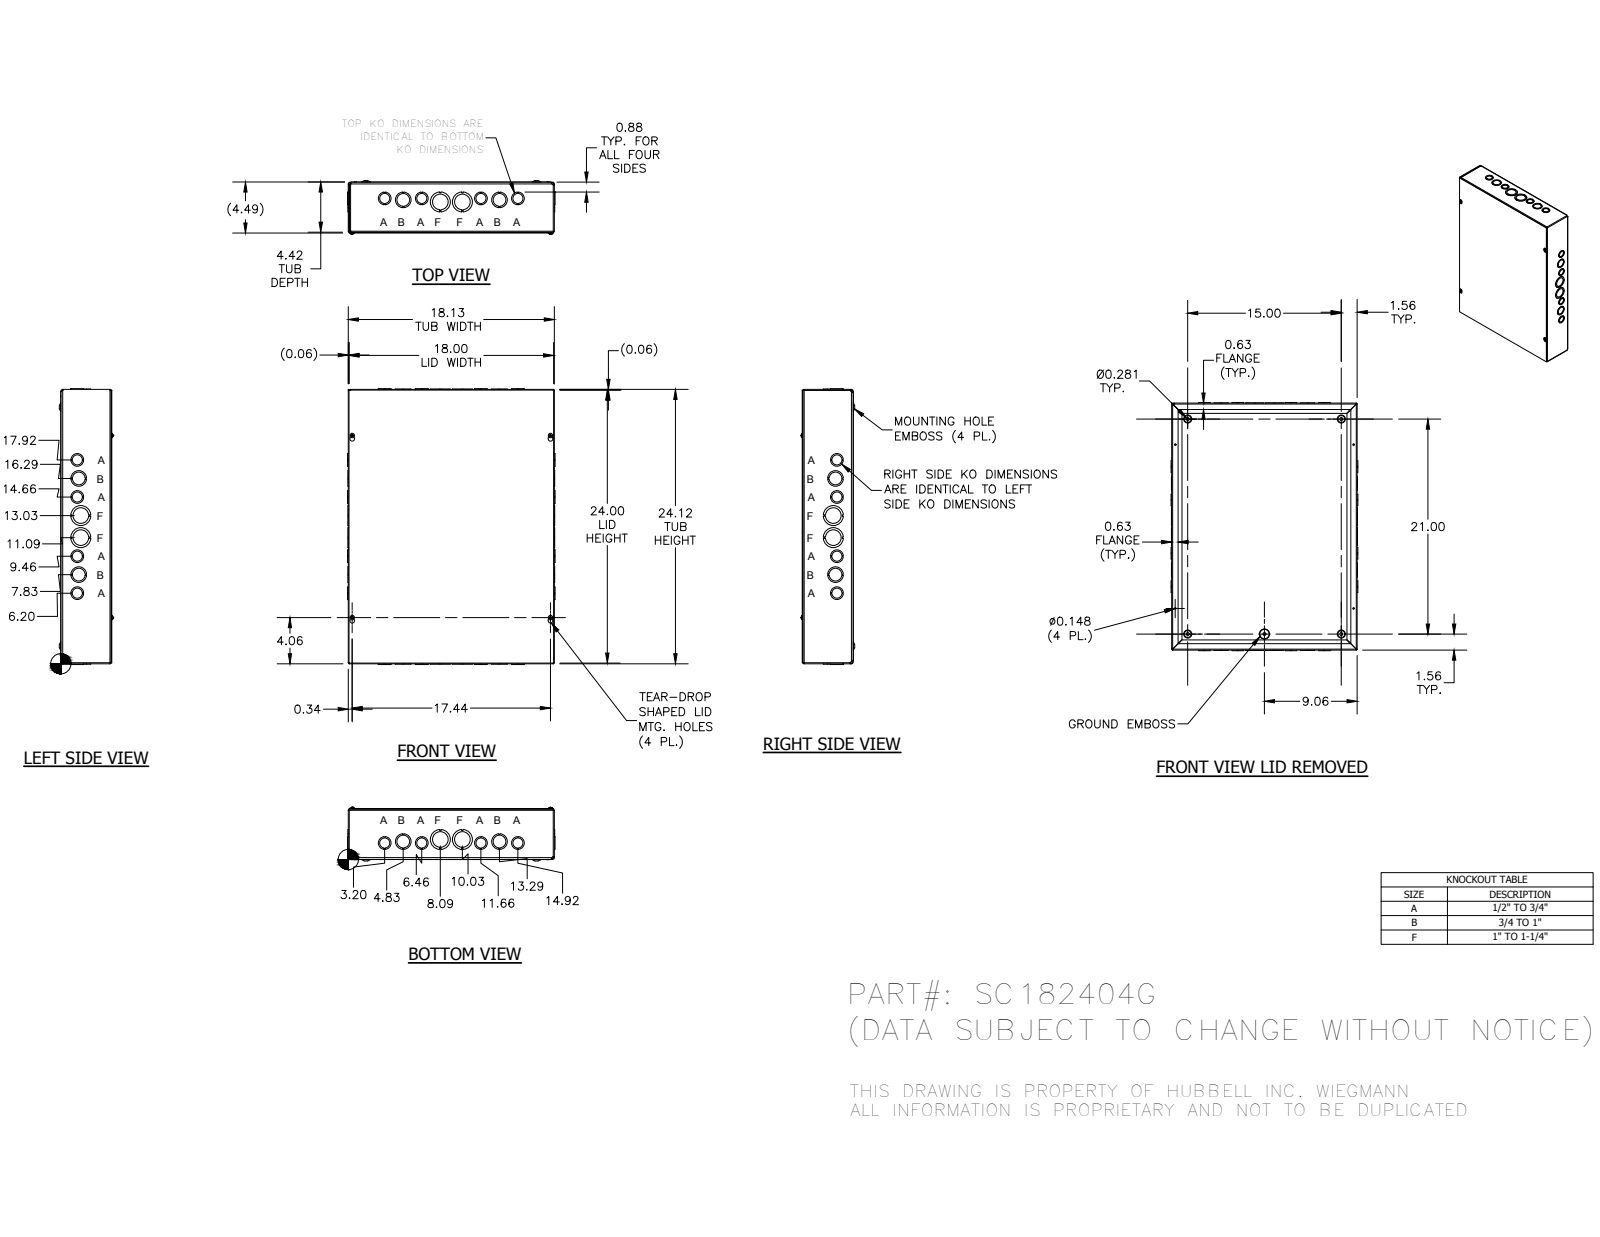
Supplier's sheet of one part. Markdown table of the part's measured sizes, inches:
| quantity | value |
| --- | --- |
| part name | SC1824GBKP; SC182404GWRA; SC1824GLID; 34056 (+1 more) |
| STEP written by | Autodesk Inventor 2014 (AUTOMOTIVE_DESIGN) |
| units | inches |
| bodies | 38 solids, 1255 faces (839 planar, 273 cylindrical, 143 other) |
| overall size | 24.249 × 18.249 × 4.716 |
| round holes (diameter × count) | 1.125 × 12, 0.875 × 8, 1.375 × 8, 0.148 × 4, 0.3 × 4, 1.75 × 4, 0.165 × 1 |
| round bosses / shafts (diameter × count) | 0.18 × 8, 0.384 × 4, 0.164 × 4, 0.228 × 1 |
| partial cylindrical surfaces (radius × count) | 0.031 × 8, 0.093 × 8, 0.055 × 4, 0.062 × 4, 0.094 × 4, 0.11 × 4, 0.117 × 4, 0.124 × 4 |
| main face-to-face distances | 0.074, 4.417, 4.343, 4.491, 0.062, 18.063, 24.063, 18.125, 18.001, 24.125 |
| hole center spacings | 1.635, 1.659, 3.265, 3.584, 5.204, 6.831, 8.46, 18.54 |
